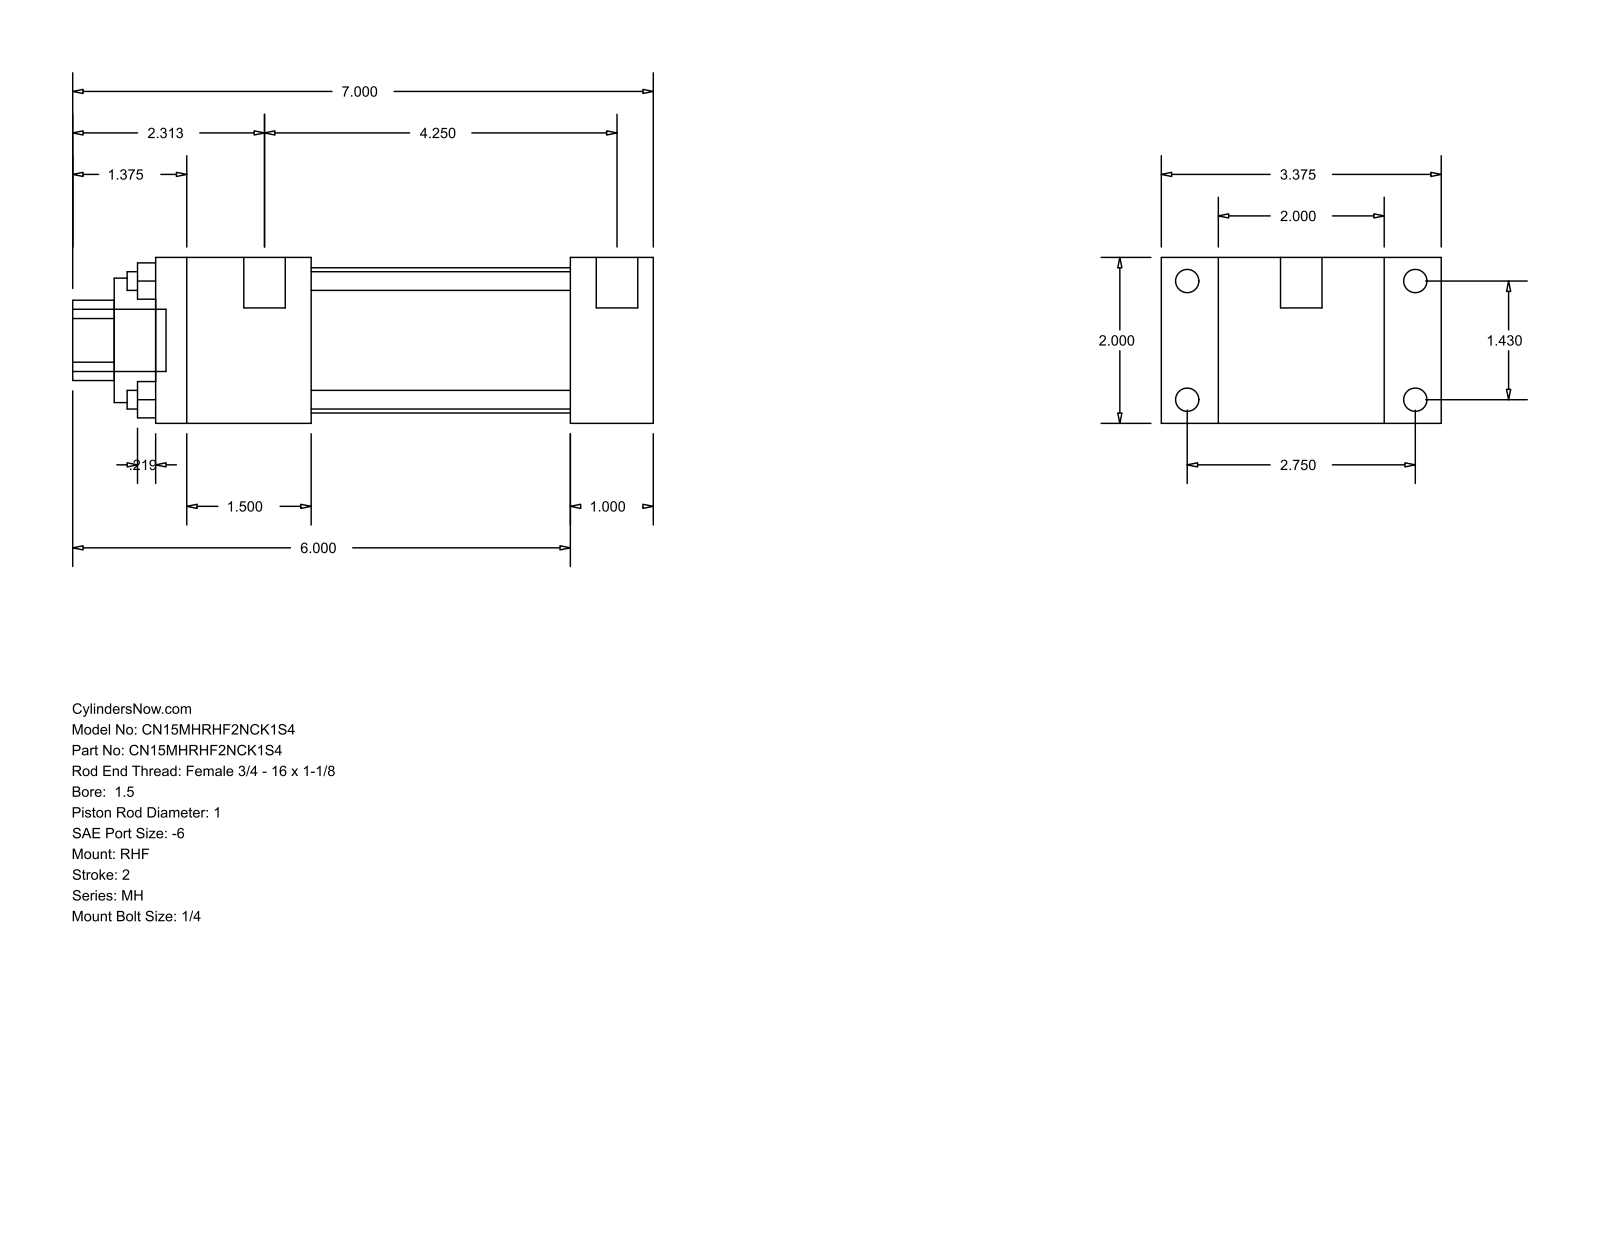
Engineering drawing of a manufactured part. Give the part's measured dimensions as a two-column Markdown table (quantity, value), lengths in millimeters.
| quantity | value |
| --- | --- |
| part name | MH_RHF__0150_1 |
| STEP written by | GSSL Pune (CONFIG_CONTROL_DESIGN) |
| units | millimeters |
| bodies | 0 solids, 88 faces (60 planar, 28 cylindrical, 0 other) |
| overall size | 177.8 × 85.72 × 50.8 |
| round holes (diameter × count) | 5.71 × 4, 25.4 × 1, 38.1 × 1, 44.45 × 1 |
| round bosses / shafts (diameter × count) | 7.14 × 4, 5.56 × 4, 12.7 × 2, 19.05 × 1 |
| partial cylindrical surfaces (radius × count) | 12.29 × 1 |
| main face-to-face distances | 50.8, 25.4, 17.46, 68.26, 85.72, 152.4, 127, 47.63, 79.37, 104.77 |
| hole center spacings | 25.68, 36.32, 51.36 |
